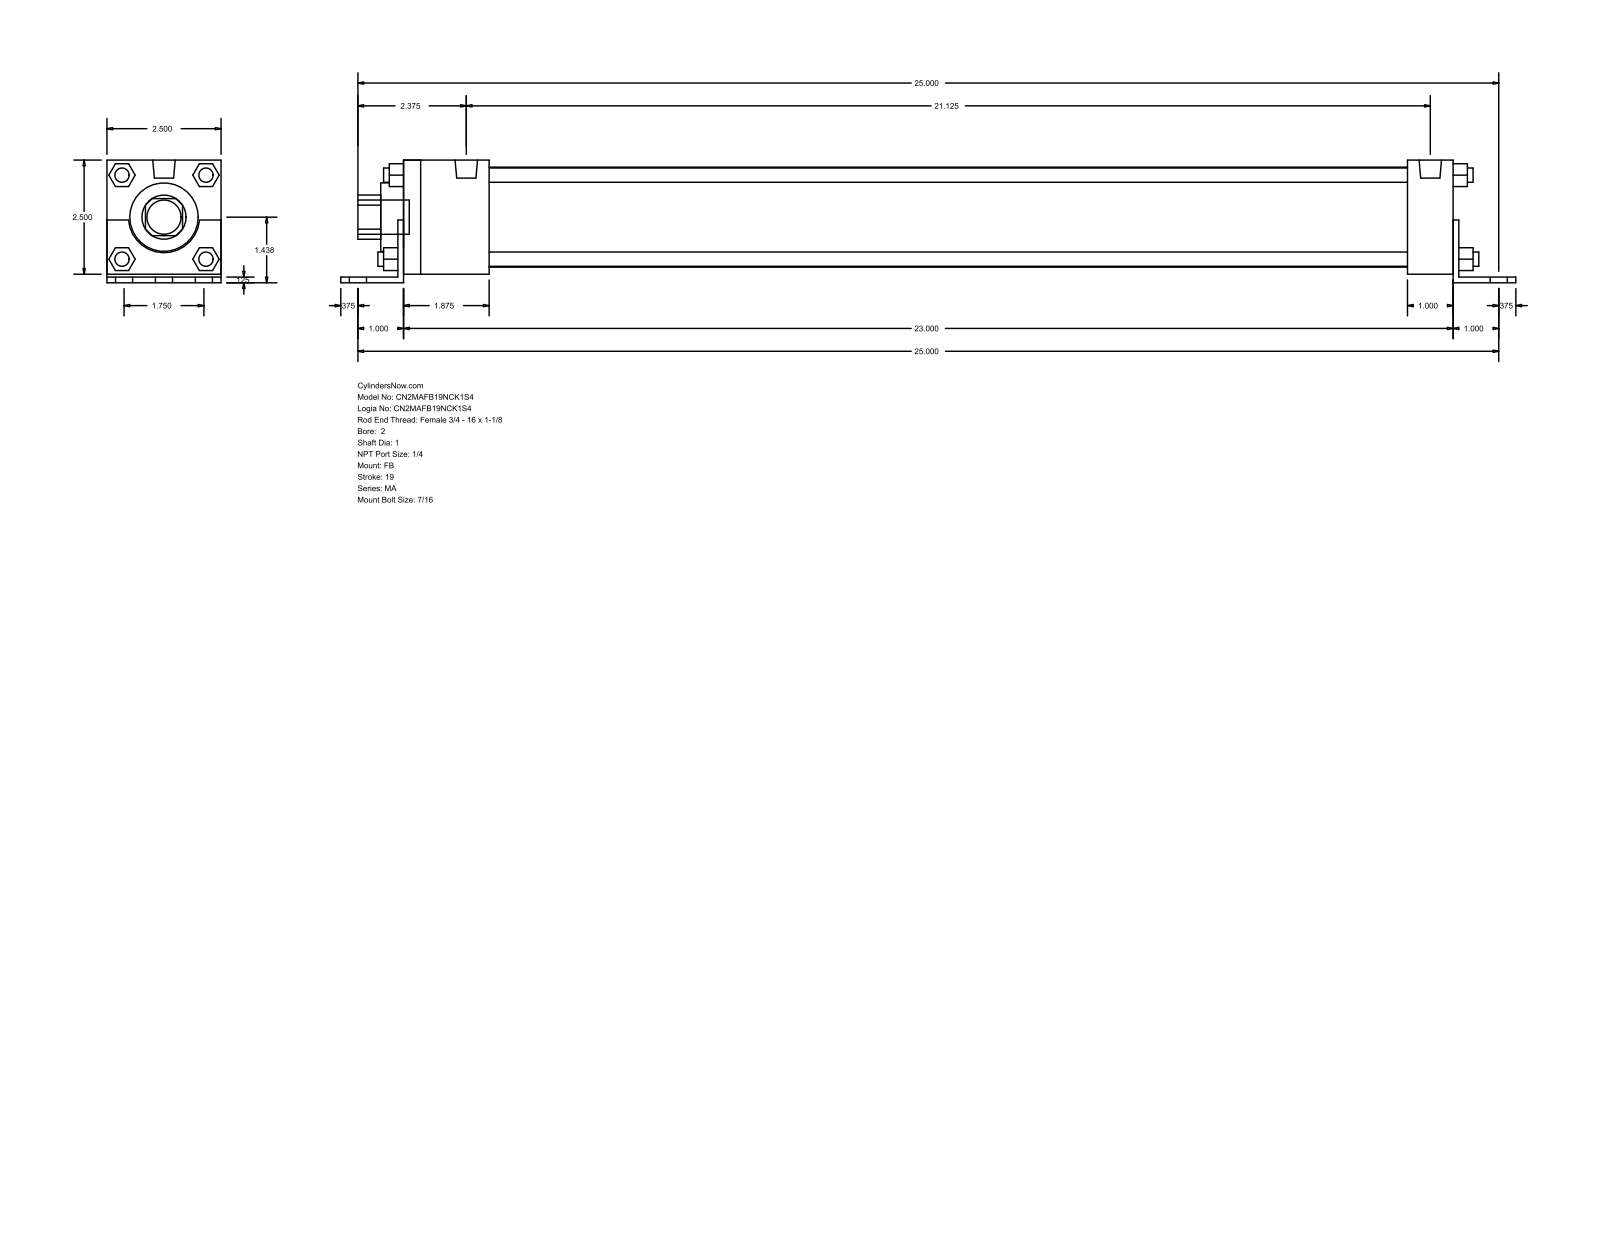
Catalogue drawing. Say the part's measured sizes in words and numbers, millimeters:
The part is named "MA_FB__0200_1". Its 3-D file was written by "GSSL Pune (CONFIG_CONTROL_DESIGN)". It is 0 solids with 140 faces: 105 planar, 35 cylindrical and 0 other. Overall it measures 654.05 by 68.26 by 63.5 millimeters. Round holes: 1 of diameter 25.4, 1 of diameter 38.1, 1 of diameter 55.63. Round bosses or shafts: 8 of diameter 7.94, 6 of diameter 11.11, 2 of diameter 12.49, 1 of diameter 19.05. Partial cylindrical surfaces (rounded edges, fillets, slot ends): 1 of radius 12.29, 1 of radius 19.81. The main face-to-face distances are 63.5, 3.17, 4.76, 68.26, 1.59, 65.09, 587.37, 12.7, 584.2, 25.4.
